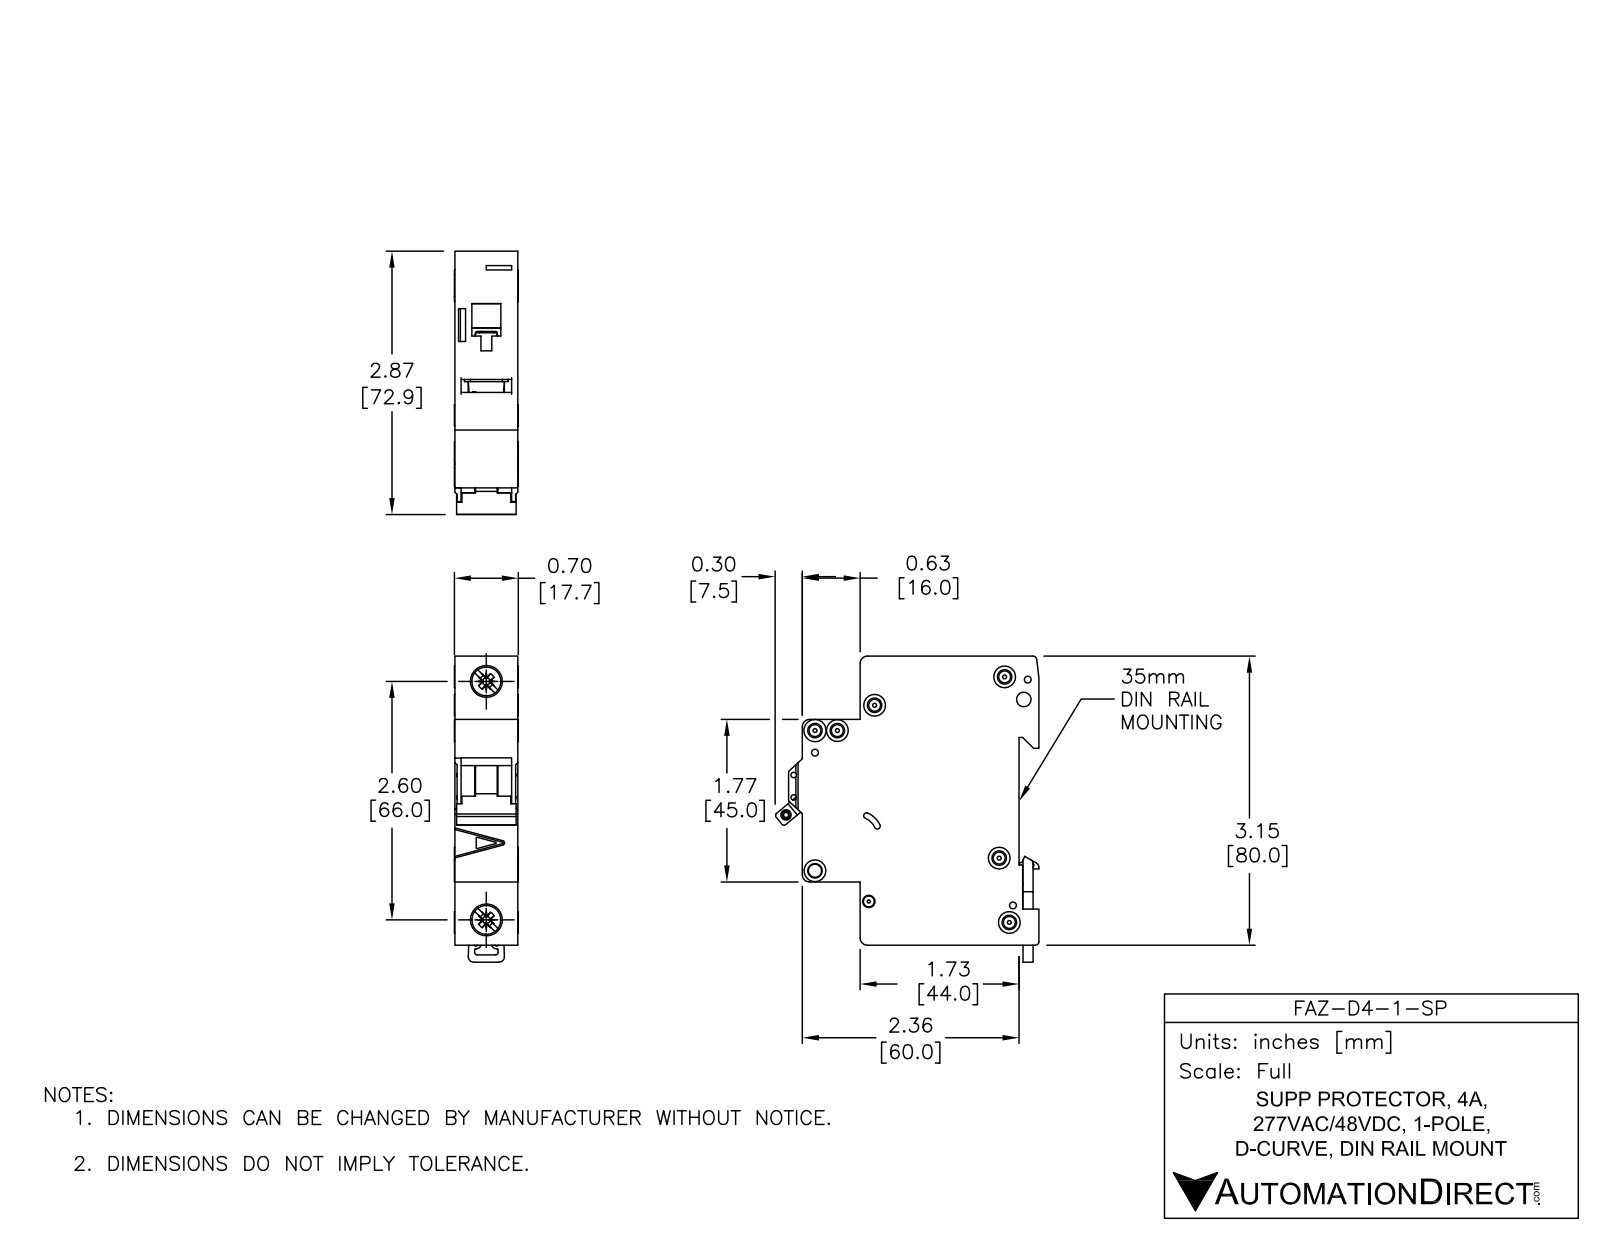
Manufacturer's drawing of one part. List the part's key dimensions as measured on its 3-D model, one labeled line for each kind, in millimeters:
Part name (STEP PRODUCT): FAZ-D4-1-SP
STEP written by: SolidWorks 2014 (AUTOMOTIVE_DESIGN)
Units: millimetres
Bodies: 5 solids, 558 faces (235 planar, 202 cylindrical, 121 other)
Overall size (bounding box): 84.78 × 73.04 × 17.7
Volume: 74 935 mm³ · Surface area: 19 545 mm²
Round holes (diameter × count): ⌀3.6 ×6, ⌀1.9 ×3, ⌀1.09 ×2, ⌀1.5 ×2, ⌀4 ×2, ⌀7.15 ×2, ⌀2.15 ×1, ⌀2.2 ×1, ⌀2.55 ×1, ⌀3.3 ×1, ⌀3.4 ×1
Round bosses / shafts (diameter × count): ⌀6 ×4, ⌀8.2 ×2, ⌀2.5 ×1
Partial cylindrical surfaces — rounded edges, fillets, slot ends (radius × count): R0.25 ×30, R0.5 ×13, R2 ×8, R0.2 ×5, R1 ×4, R0.8 ×2, R3 ×2, R1.5 ×1
Main face-to-face distances: 17.5, 79.48, 5.5, 49.5, 44, 65.5, 60, 16, 1.75, 15.75
Hole centre spacings: 6.2, 13.64, 4.81, 5.19, 5.61, 6.1, 6.44, 8.19
